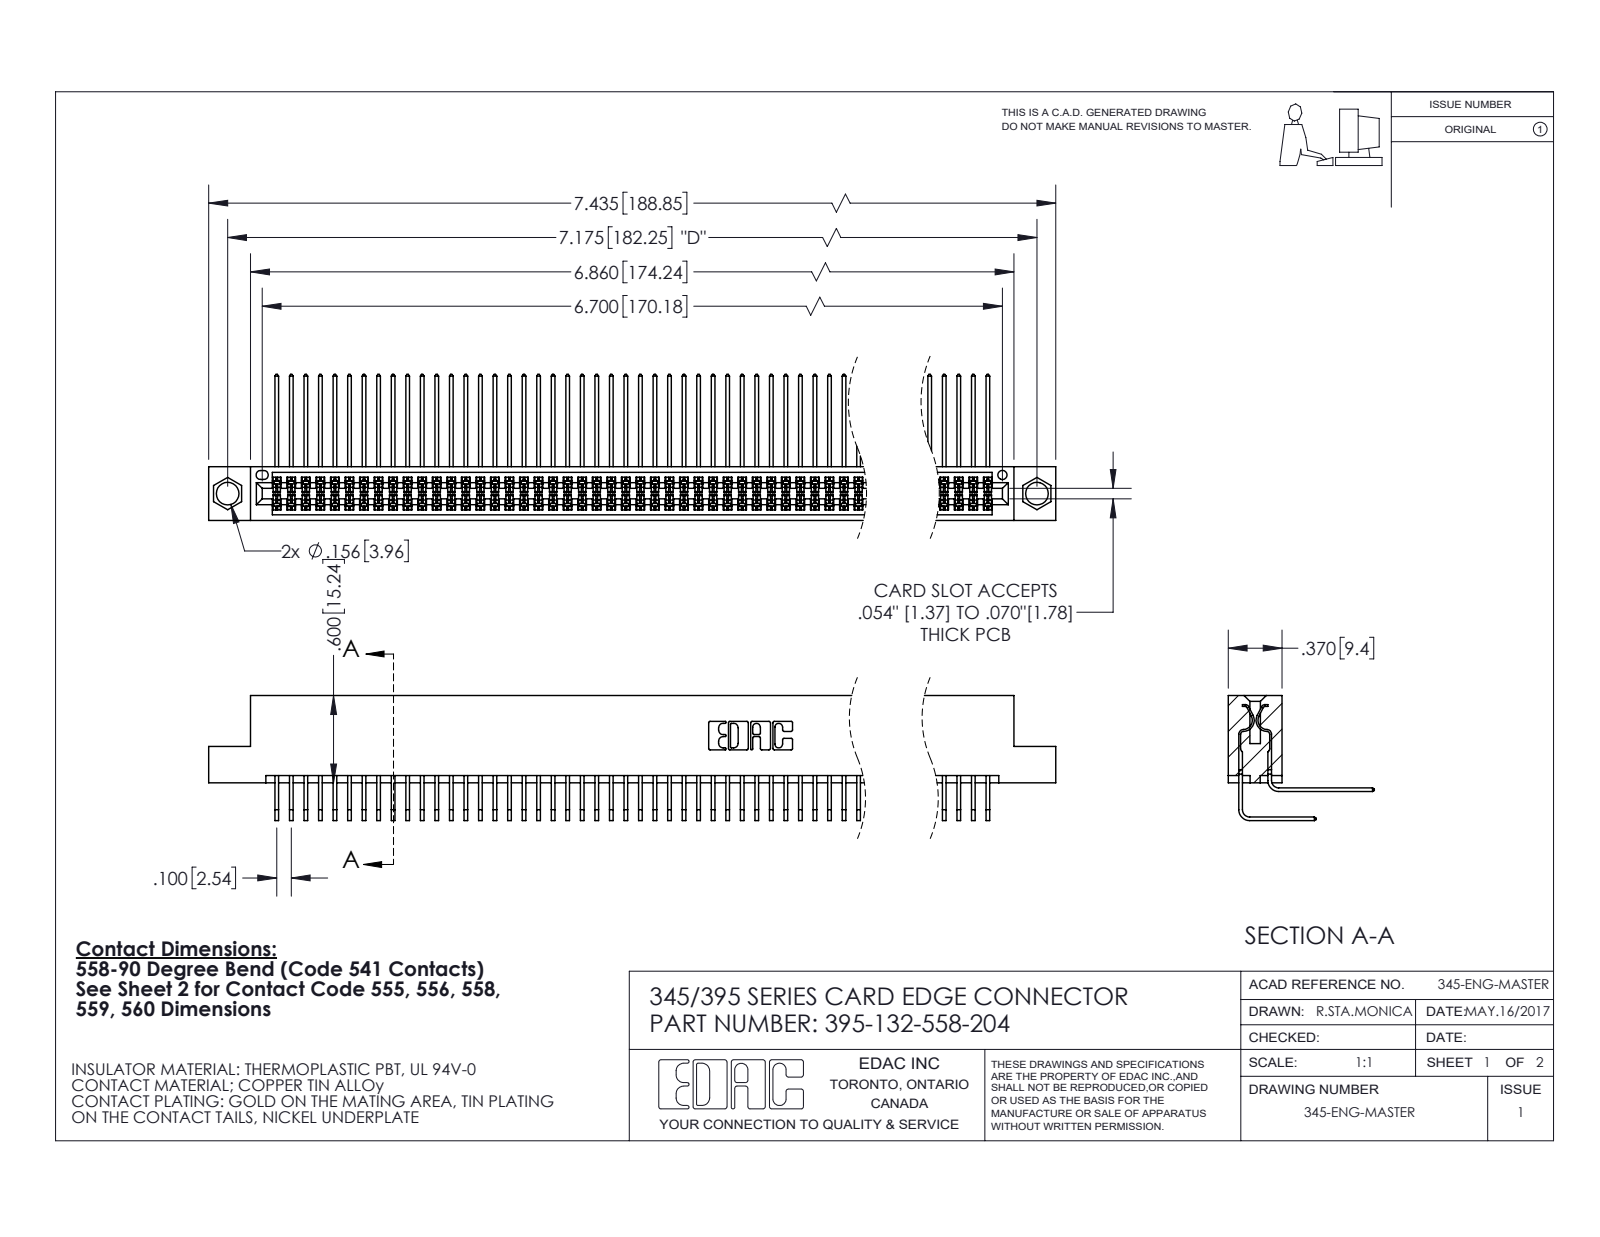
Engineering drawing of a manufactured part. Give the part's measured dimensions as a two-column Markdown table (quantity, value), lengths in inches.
| quantity | value |
| --- | --- |
| part name | 345-292-001_558 559 Tail - 1; 345 Part_Flush Mounting Lugs - 0.156 Dia-TI; 345-292-001_558 Tail - 2; 395-132-558-204 |
| STEP written by | SolidWorks 2020 (CONFIG_CONTROL_DESIGN) |
| units | inches |
| bodies | 133 solids, 7004 faces (4714 planar, 2290 cylindrical, 0 other) |
| overall size | 7.435 × 1.005 × 0.859 |
| volume | 1.173 in³ |
| surface area | 50.08 in² |
| round holes (diameter × count) | 0.156 × 2, 0.064 × 1 |
| partial cylindrical surfaces (radius × count) | 0.006 × 198, 0.01 × 22, 0.007 × 6, 0.031 × 6, 0.026 × 3, 0.014 × 2, 0.019 × 2, 0.022 × 2 |
| main face-to-face distances | 0.072, 0.298, 0.2, 0.37, 0.098, 0.272, 0.025, 0.225, 0.025, 0.175 |
| hole center spacings | 0.27, 6.939, 7.175 |
